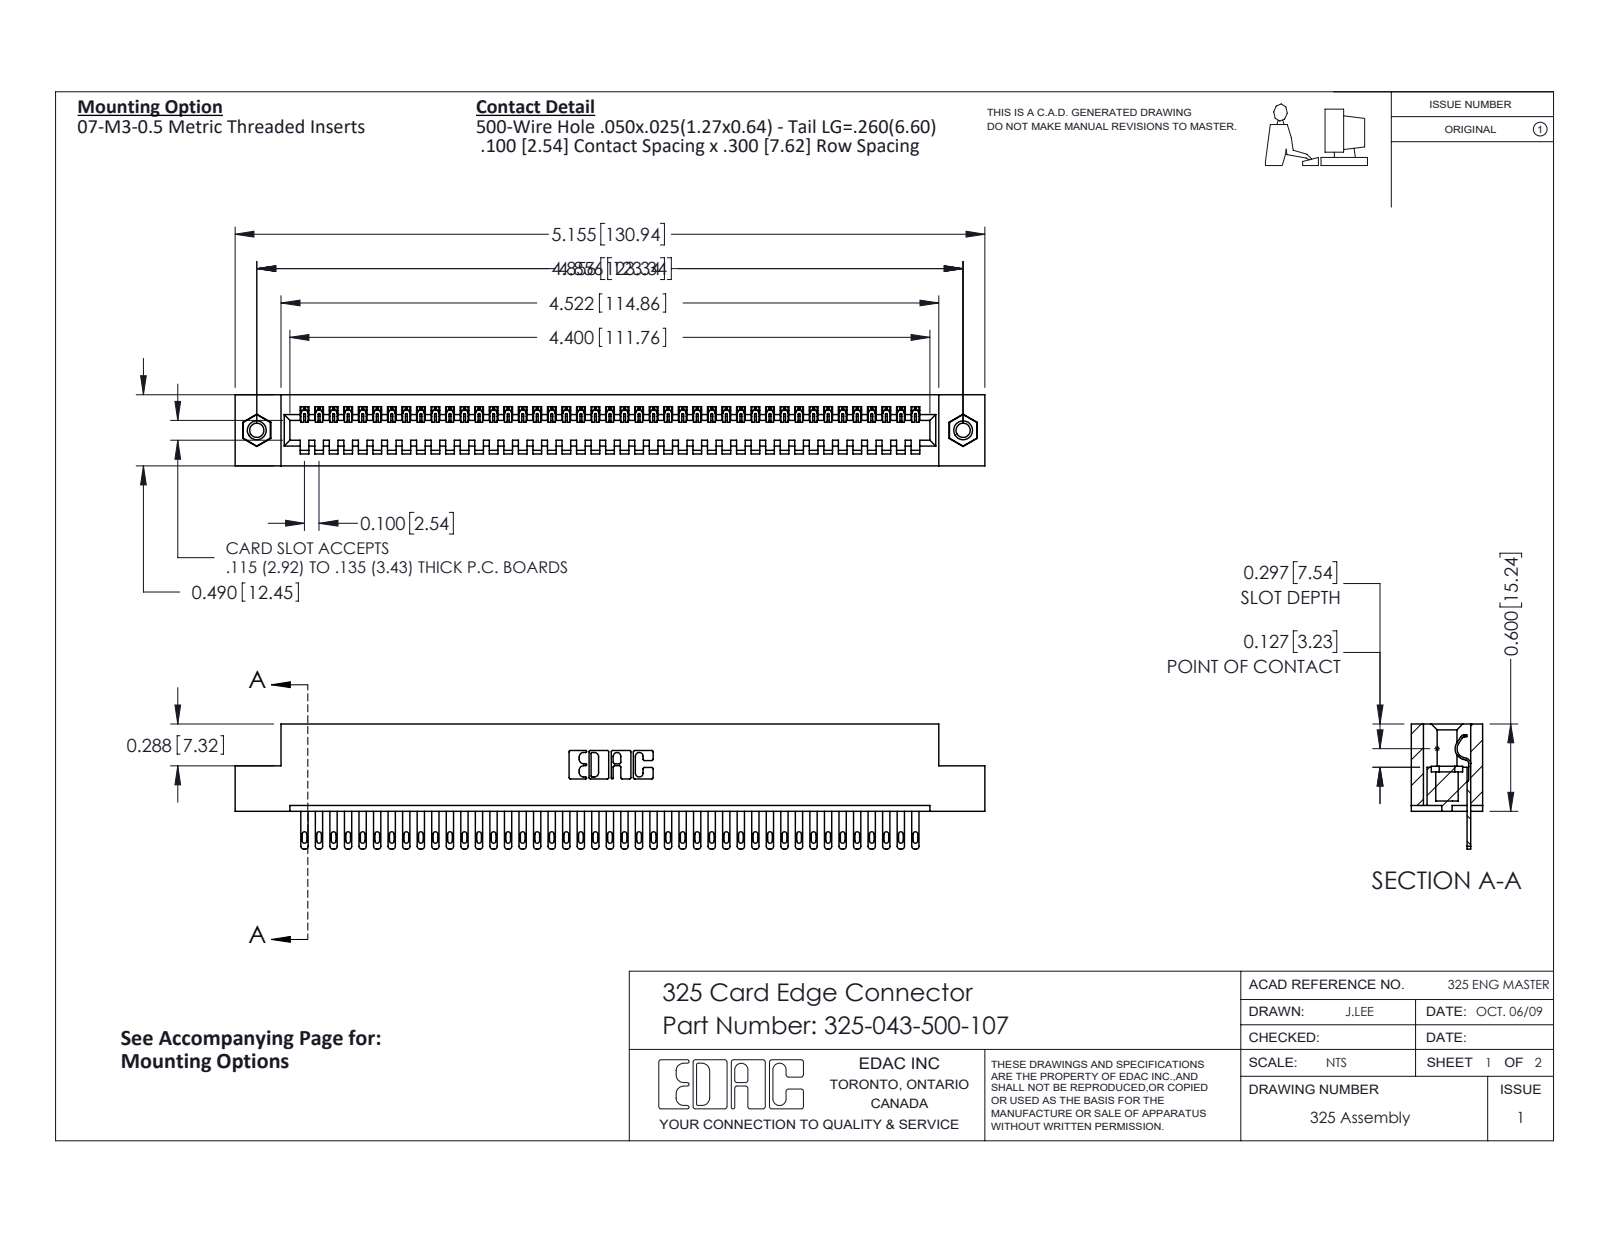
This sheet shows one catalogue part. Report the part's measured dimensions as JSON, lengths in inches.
{"part_name": "325-292-001_325-293-100; 325-043-500-107; 345-250-001_345-250-005-103; 325 Part_TI", "step_written_by": "SolidWorks 2016 (CONFIG_CONTROL_DESIGN)", "units": "inches", "bodies": {"solids": 46, "faces": 2496, "planar": 1650, "cylindrical": 830, "other": 16}, "overall_size": [5.155, 0.86, 0.49], "volume_in3": 1.016, "surface_area_in2": 28.41, "round_holes": [[0.098, 2], [0.125, 2], [0.16, 2]], "round_bosses_or_shafts": [[0.155, 2]], "partial_cylinders_radius": [[0.006, 86], [0.016, 86], [0.02, 86], [0.01, 22], [0.007, 6], [0.031, 6], [0.026, 3], [0.014, 1]], "face_to_face_distances": [0.083, 0.407, 0.49, 0.3, 0.107, 0.383, 0.025, 0.325, 0.56, 0.04], "hole_center_spacings": [4.856]}
